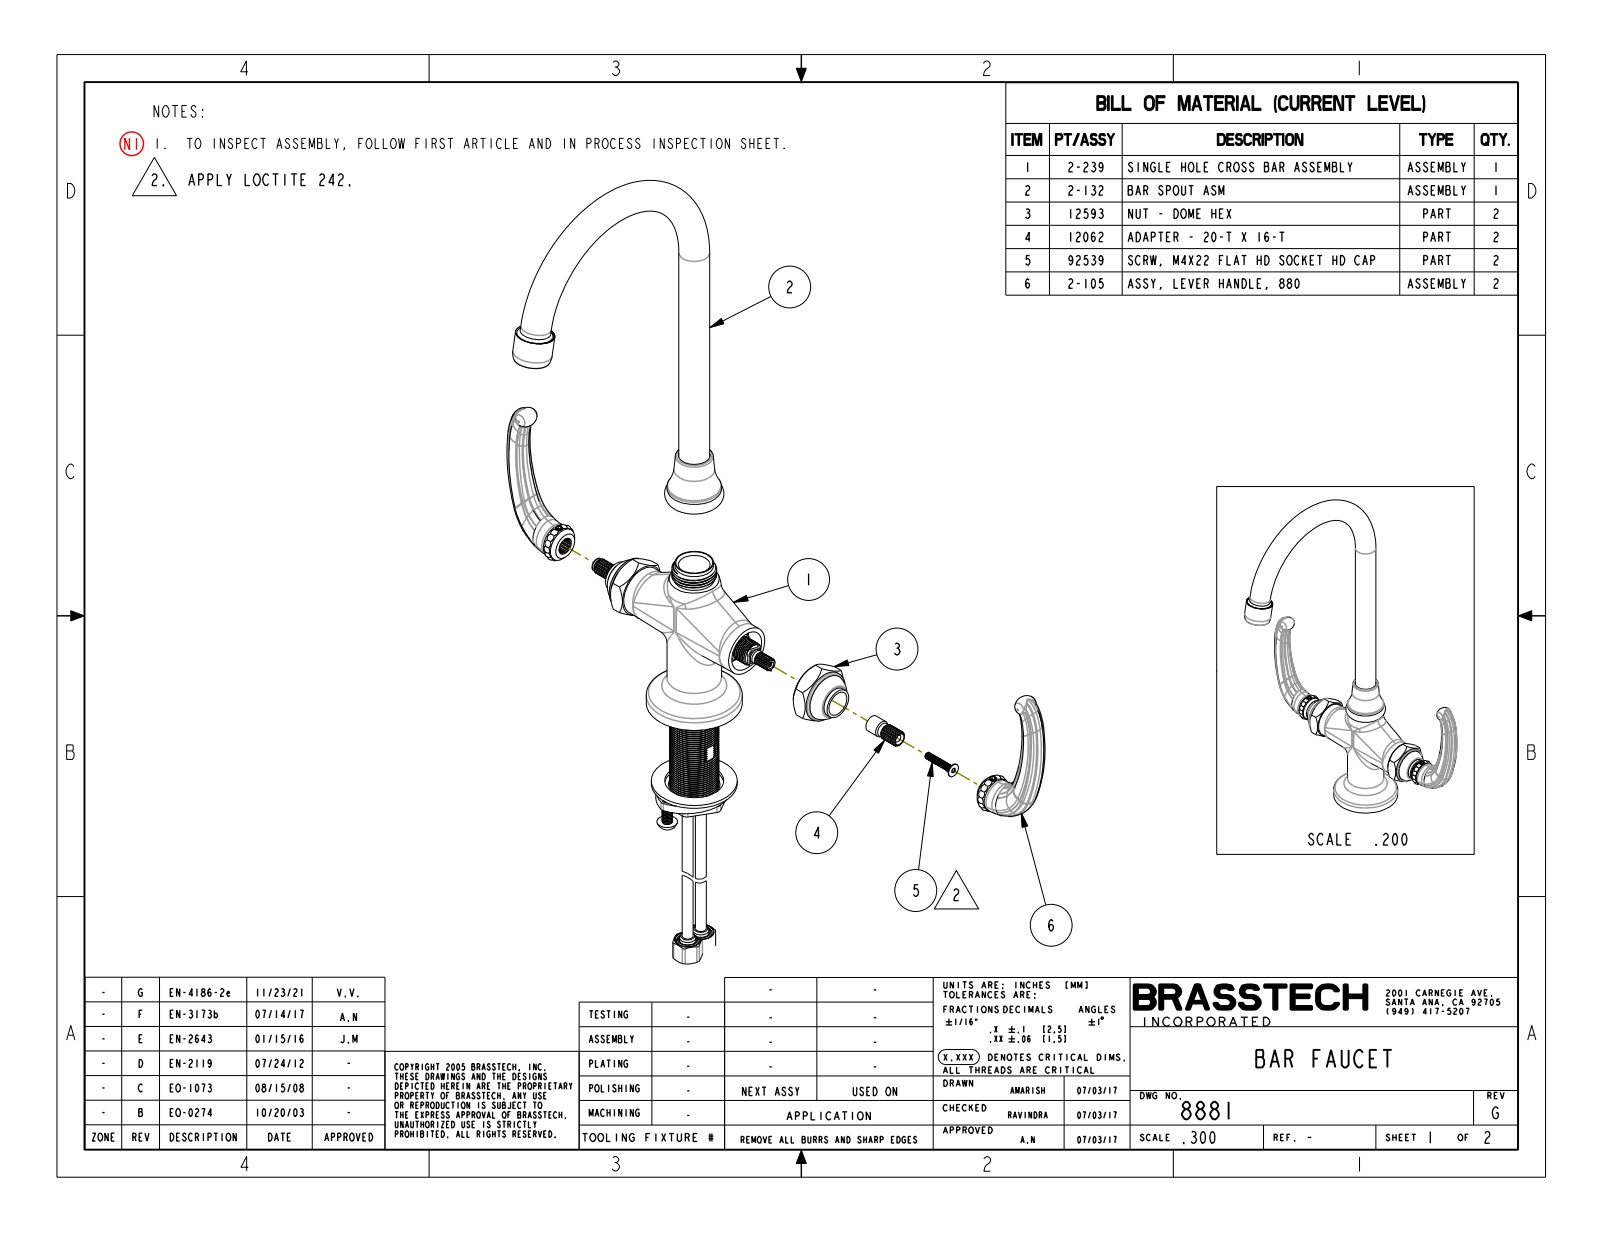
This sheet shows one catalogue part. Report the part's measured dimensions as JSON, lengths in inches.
{"part_name": "10230; 1-204; 1-205; 10515 (+8 more)", "step_written_by": "PRO/ENGINEER BY PARAMETRIC TECHNOLOGY CORPORATION, 2009300 (CONFIG_CONTROL_DESIGN)", "units": "inches", "bodies": {"solids": 18, "faces": 3463, "planar": 453, "cylindrical": 826, "other": 2184}, "overall_size": [13.31, 8.508, 6.799], "volume_in3": 12.91, "surface_area_in2": 283.2, "round_holes": [[0.25, 3], [0.136, 2], [0.196, 2], [0.351, 2], [0.423, 2], [0.642, 2], [0.201, 1], [0.266, 1], [0.339, 1], [0.391, 1], [0.44, 1], [0.481, 1]], "round_bosses_or_shafts": [[0.706, 2], [0.164, 2], [2.2, 1], [1.646, 1], [1.25, 1], [1.248, 1], [1.215, 1], [1.17, 1]], "partial_cylinders_radius": [[0.04, 9], [0.08, 8], [0.26, 2], [0.3, 2], [0.164, 1], [0.187, 1]], "face_to_face_distances": [1.25, 1.301, 2.509, 0.1, 0.28, 0.866, 2.354, 0.255, 3.555, 1.046], "hole_center_spacings": [0.311, 0.617, 0.455, 0.6, 2.377, 2.392, 2.675, 2.69]}
